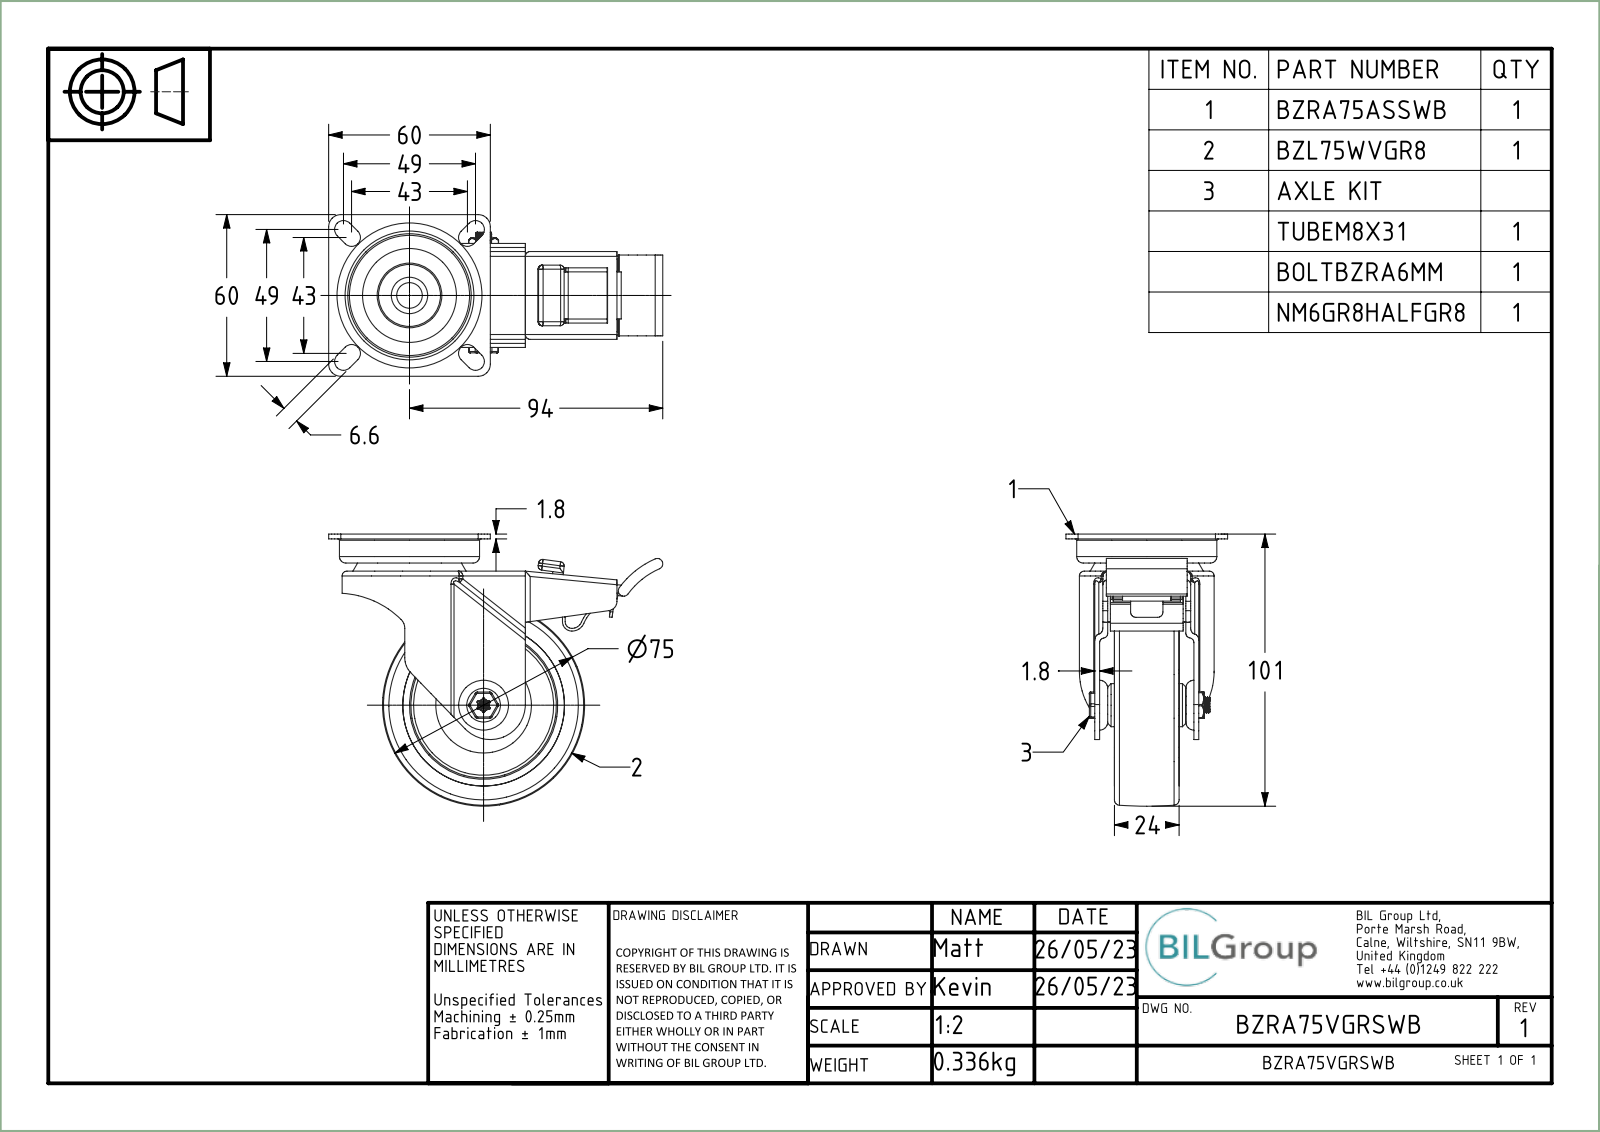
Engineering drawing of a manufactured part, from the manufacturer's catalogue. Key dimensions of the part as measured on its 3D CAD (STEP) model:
Part name (STEP PRODUCT): BZRA75ASSWB; ZINC PLATED PRESSED STEEL TOP PLATE; ZINC PLATED PRESSED STEEL FORKS; ZINC PLATED PRESSED STEEL BRAKE (+8 more)
STEP written by: Spatial InterOp 3D (CONFIG_CONTROL_DESIGN)
Units: millimetres
Bodies: 10 solids, 710 faces (237 planar, 291 cylindrical, 182 other)
Overall size (bounding box): 124 × 101 × 60
Volume: 110 991 mm³ · Surface area: 74 792 mm²
Round holes (diameter × count): ⌀6 ×1, ⌀6.4 ×1, ⌀6.5 ×1, ⌀8.4 ×1, ⌀8.5 ×1, ⌀9.5 ×1, ⌀41.95 ×1, ⌀47.8 ×1, ⌀54 ×1, ⌀60 ×1
Round bosses / shafts (diameter × count): ⌀52 ×1, ⌀39 ×1, ⌀16 ×1, ⌀15 ×1, ⌀13.5 ×1, ⌀8 ×1, ⌀5 ×1
Partial cylindrical surfaces — rounded edges, fillets, slot ends (radius × count): R1 ×22, R1.8 ×22, R0.5 ×12, R1.5 ×11, R0.9 ×10, R3.3 ×8, R0.4 ×6, R2 ×5
Main face-to-face distances: 1.8, 33.8, 3, 2.5, 12.5, 10, 26.5, 14, 16.5, 4.8
